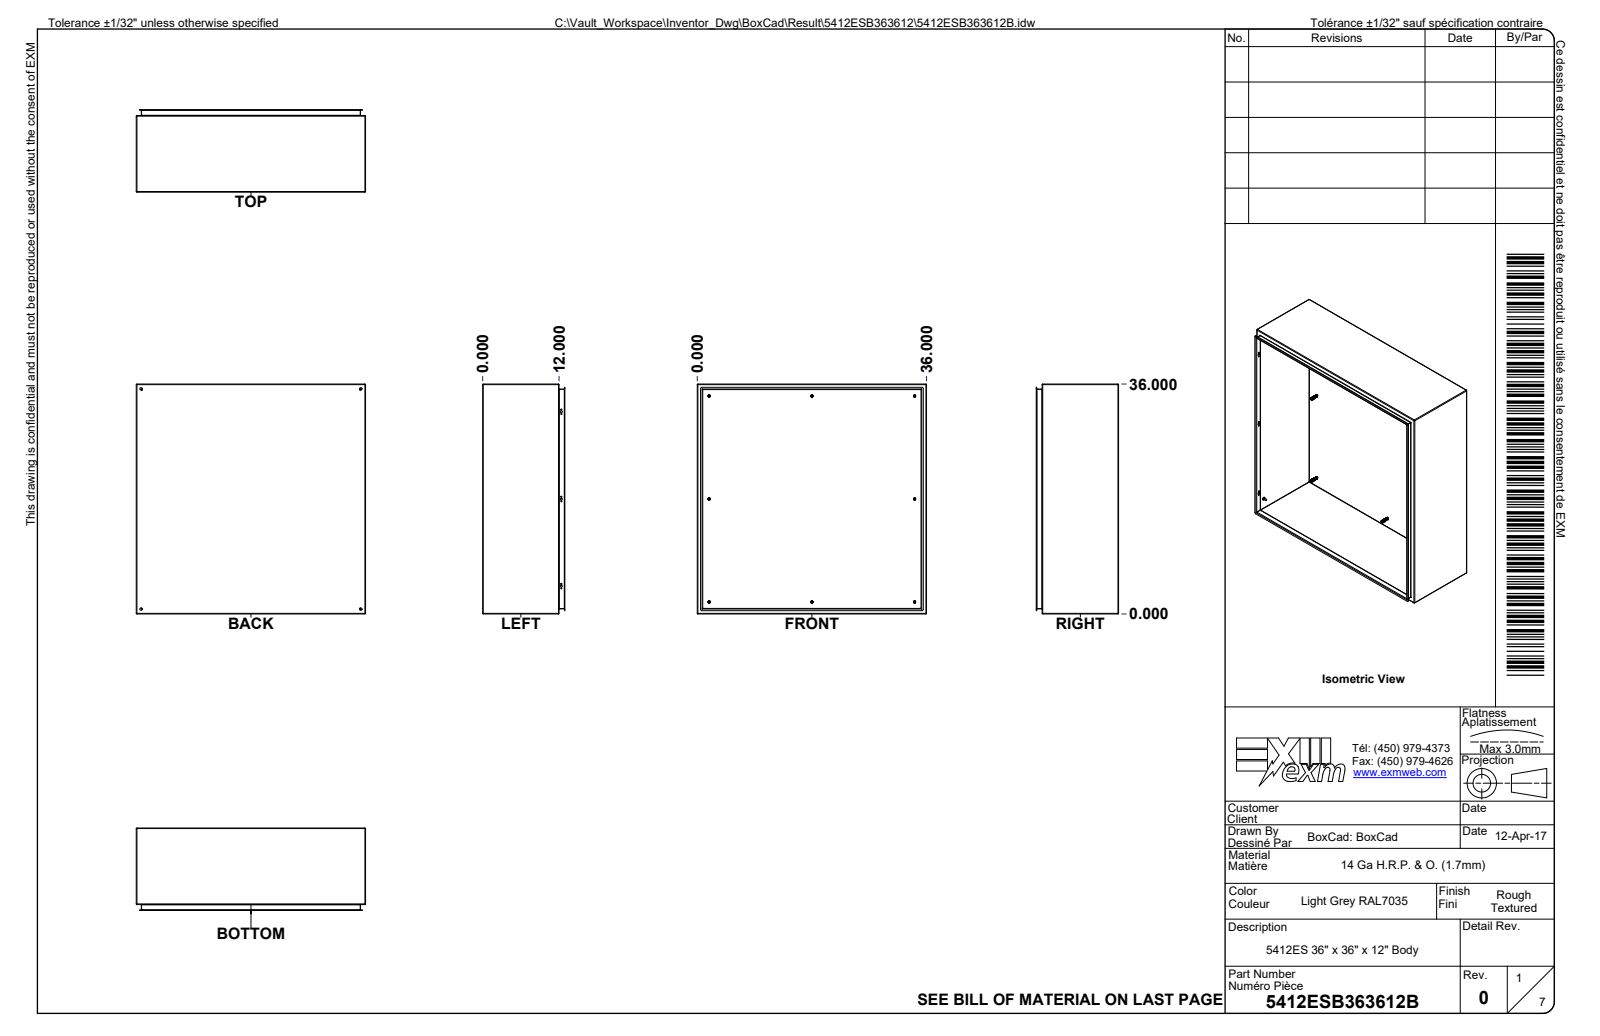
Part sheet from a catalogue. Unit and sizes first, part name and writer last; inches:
Units: inches
Overall size (bounding box): 36.018 × 36 × 13.295
Round holes (diameter × count): ⌀0.165 ×64, ⌀0.03 ×14, ⌀0.043 ×12, ⌀0.315 ×12, ⌀0.201 ×11, ⌀0.27 ×8, ⌀0.311 ×8, ⌀0.178 ×6, ⌀0.5 ×5, ⌀0.197 ×4, ⌀0.268 ×4, ⌀0.29 ×4
Round bosses / shafts (diameter × count): ⌀0.237 ×64, ⌀0.03 ×14, ⌀0.232 ×13, ⌀0.039 ×12, ⌀0.717 ×8, ⌀0.311 ×8, ⌀0.262 ×8, ⌀0.177 ×5
Partial cylindrical surfaces — rounded edges, fillets, slot ends (radius × count): R0.02 ×439, R0.01 ×243, R0.039 ×184, R0.008 ×156, R0.012 ×92, R0.016 ×44, R0.016 ×36, R0.031 ×32
Main face-to-face distances: 0.068, 13.052, 35.932, 12.983, 13.12, 0.942, 0.874, 12.109, 12.178, 1.047
Hole centre spacings: 13.652, 1.969, 16.125, 17.287, 33.394, 36.056, 37.569, 0.984
Volume: 466.9 in³ · Surface area: 12 329 in²
Bodies: 103 solids, 17863 faces (5759 planar, 4326 cylindrical, 7778 other)
Part name (STEP PRODUCT): 5412ESB363612; 5412ESB363612B; 5412ESB363612B-P; STK-Q-16005 (+8 more)
STEP written by: Autodesk Inventor 2024 (AUTOMOTIVE_DESIGN)
